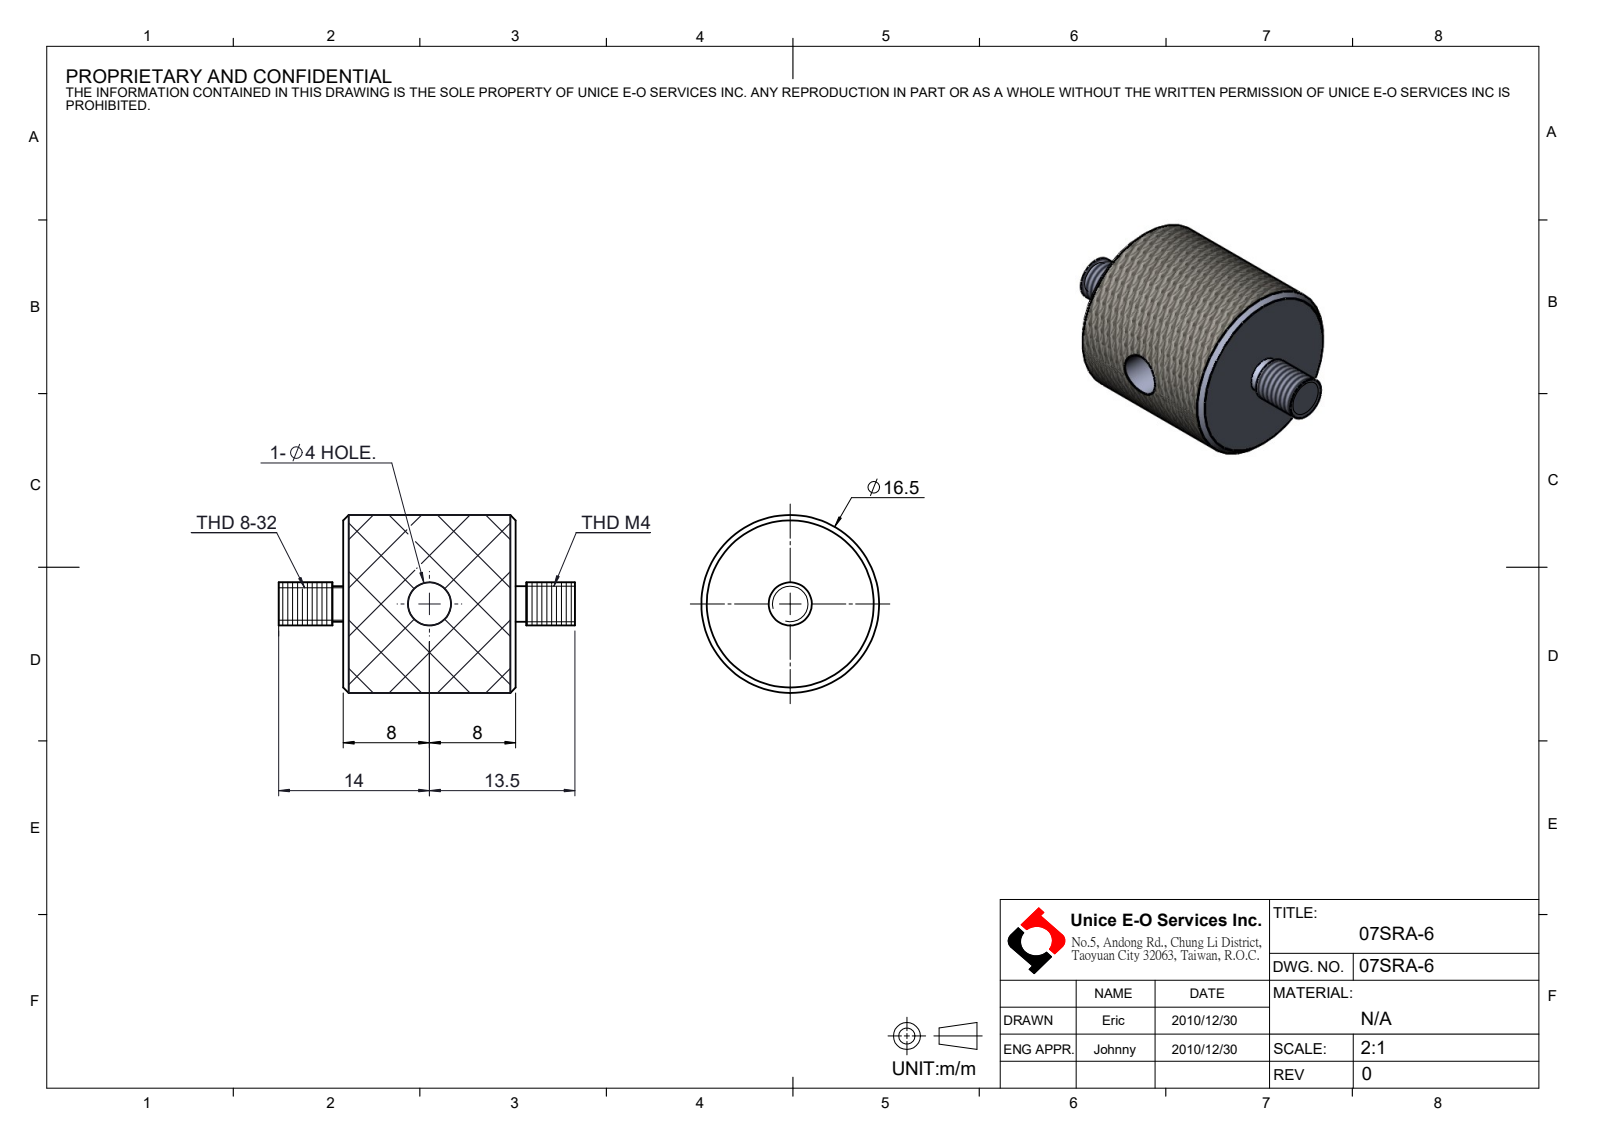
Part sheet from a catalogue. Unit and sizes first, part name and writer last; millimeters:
Units: millimetres
Overall size (bounding box): 27.5 × 16.5 × 16.5
Round holes (diameter × count): ⌀4 ×1
Round bosses / shafts (diameter × count): ⌀16.5 ×1, ⌀4 ×1, ⌀3.3 ×1
Main face-to-face distances: 16, 5.5, 21.5, 27.5, 22, 6, 1, 17, 22.5, 5
Volume: 3 339 mm³ · Surface area: 1 561 mm²
Bodies: 1 solid, 22 faces (6 planar, 12 cylindrical, 4 other)
Part name (STEP PRODUCT): 07SRA-6
STEP written by: SolidWorks 2016 (CONFIG_CONTROL_DESIGN)
